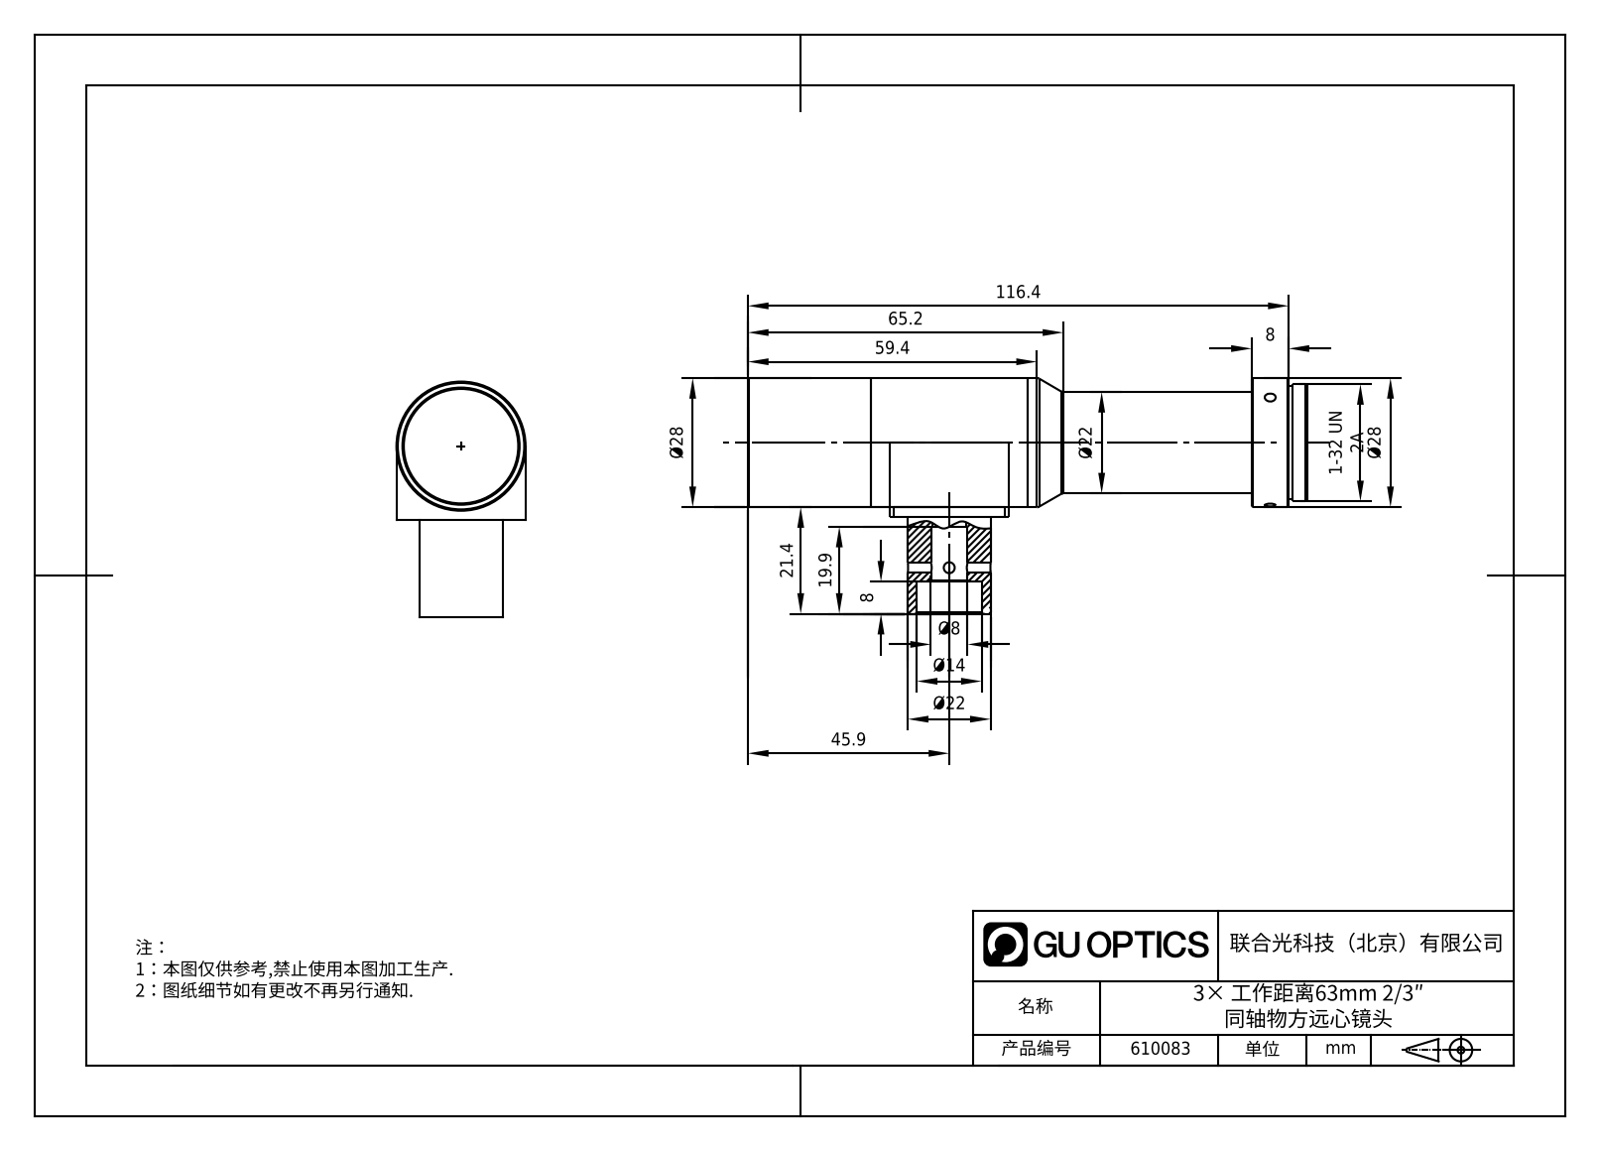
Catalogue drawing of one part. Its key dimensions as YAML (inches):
part_name: "WWH30-63CTV3"
step_written_by: "SolidWorks 2017 (CONFIG_CONTROL_DESIGN)"
units: inches
bodies: {solids: 1, faces: 40, planar: 13, cylindrical: 13, other: 14}
overall_size: [4.74, 1.945, 1.102]
volume: 4.46
surface_area: 20.44
round_bosses_or_shafts:
  - {diameter: 0.866, count: 2}
  - {diameter: 1.102, count: 1}
  - {diameter: 1, count: 1}
  - {diameter: 0.961, count: 1}
face_to_face_distances: [4.74, 1.102, 0.843, 4.268, 0.472, 4.583, 0.315, 0.157, 1.295, 2.319]
